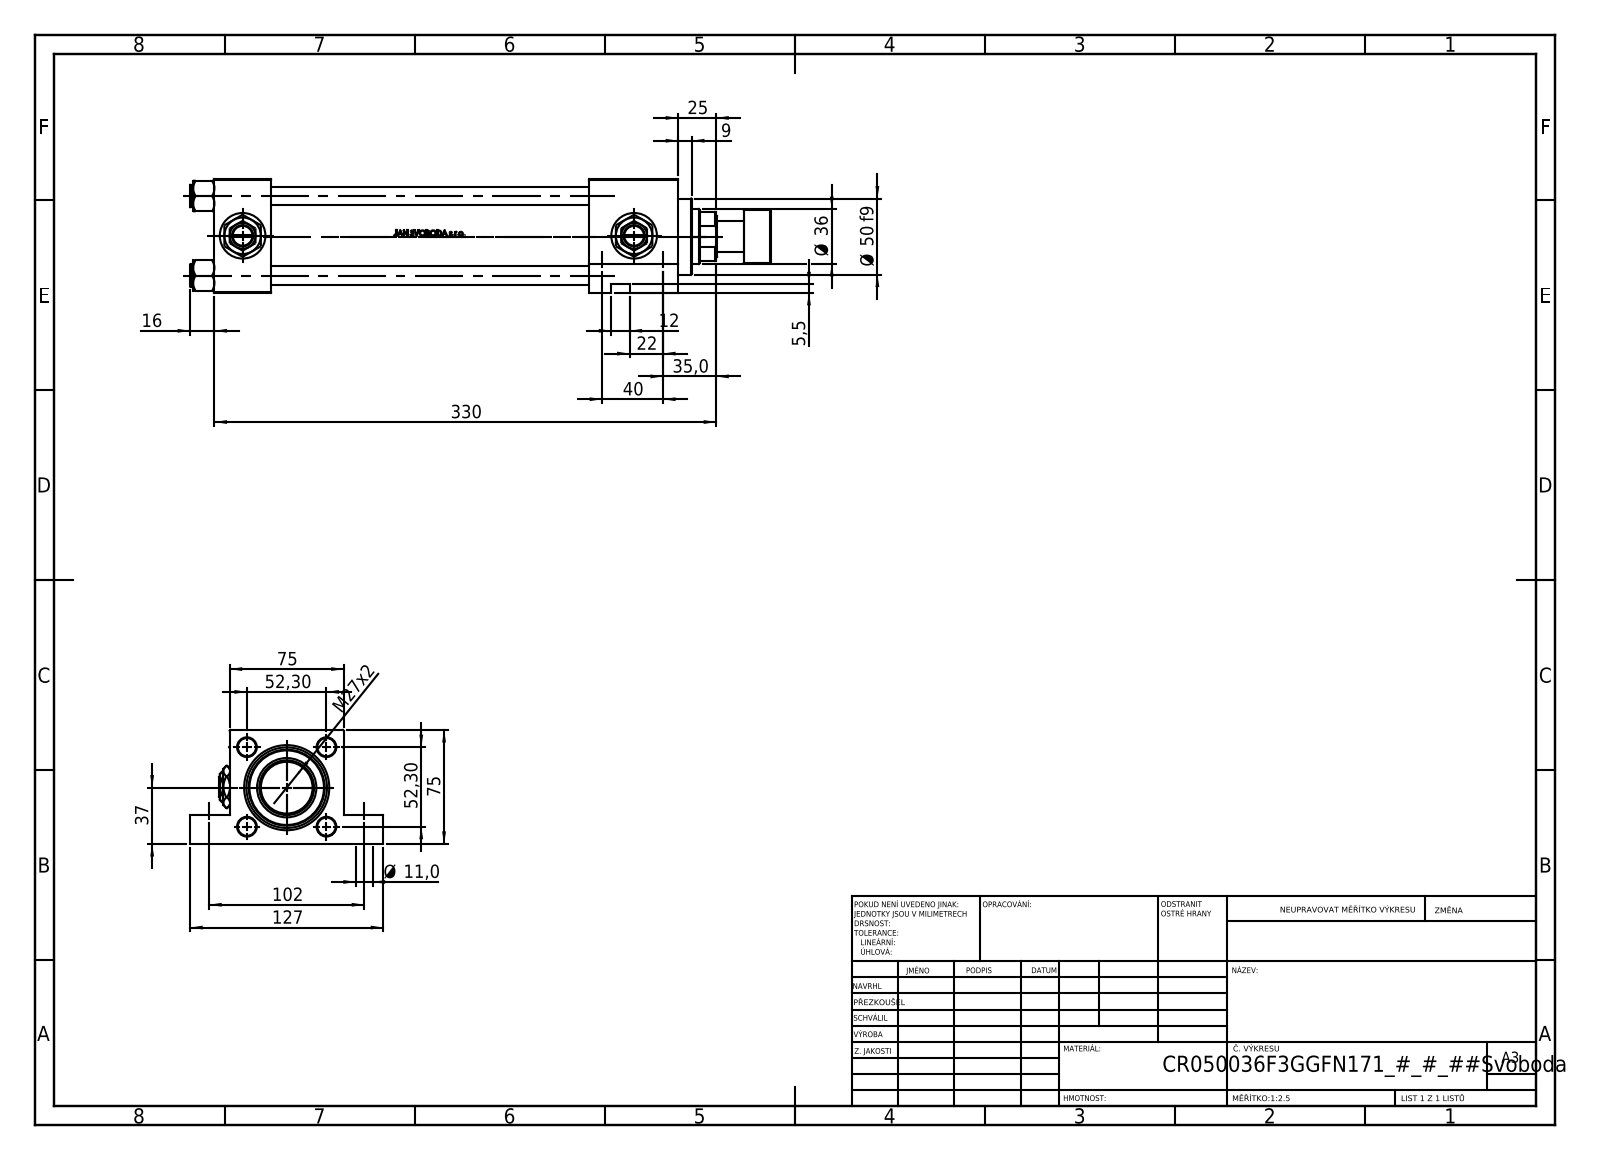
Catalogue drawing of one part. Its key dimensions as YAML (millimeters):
part_name: "NUT_M5_F; Zatka_pro_OIL_PORT; V215_VC_A; V215CR_F_Body (+3 more)"
step_written_by: "SolidWorks 2019 (CONFIG_CONTROL_DESIGN)"
units: millimeters
bodies: {solids: 14, faces: 1216, planar: 488, cylindrical: 140, other: 588}
overall_size: [382, 127, 75]
volume: 1051000
surface_area: 264672
round_holes:
  - {diameter: 11, count: 4}
  - {diameter: 12, count: 4}
  - {diameter: 20.96, count: 4}
  - {diameter: 30, count: 4}
  - {diameter: 7, count: 3}
  - {diameter: 25.5, count: 1}
  - {diameter: 36, count: 1}
  - {diameter: 39, count: 1}
  - {diameter: 41, count: 1}
  - {diameter: 53, count: 1}
round_bosses_or_shafts:
  - {diameter: 15, count: 4}
  - {diameter: 56, count: 1}
  - {diameter: 50, count: 1}
  - {diameter: 35, count: 1}
  - {diameter: 21, count: 1}
face_to_face_distances: [75, 37, 246, 209, 59, 305, 268, 19, 56, 74.8]
hole_center_spacings: [52.3, 36.63, 37.34, 40, 51.62, 60.21, 73.96, 102]
